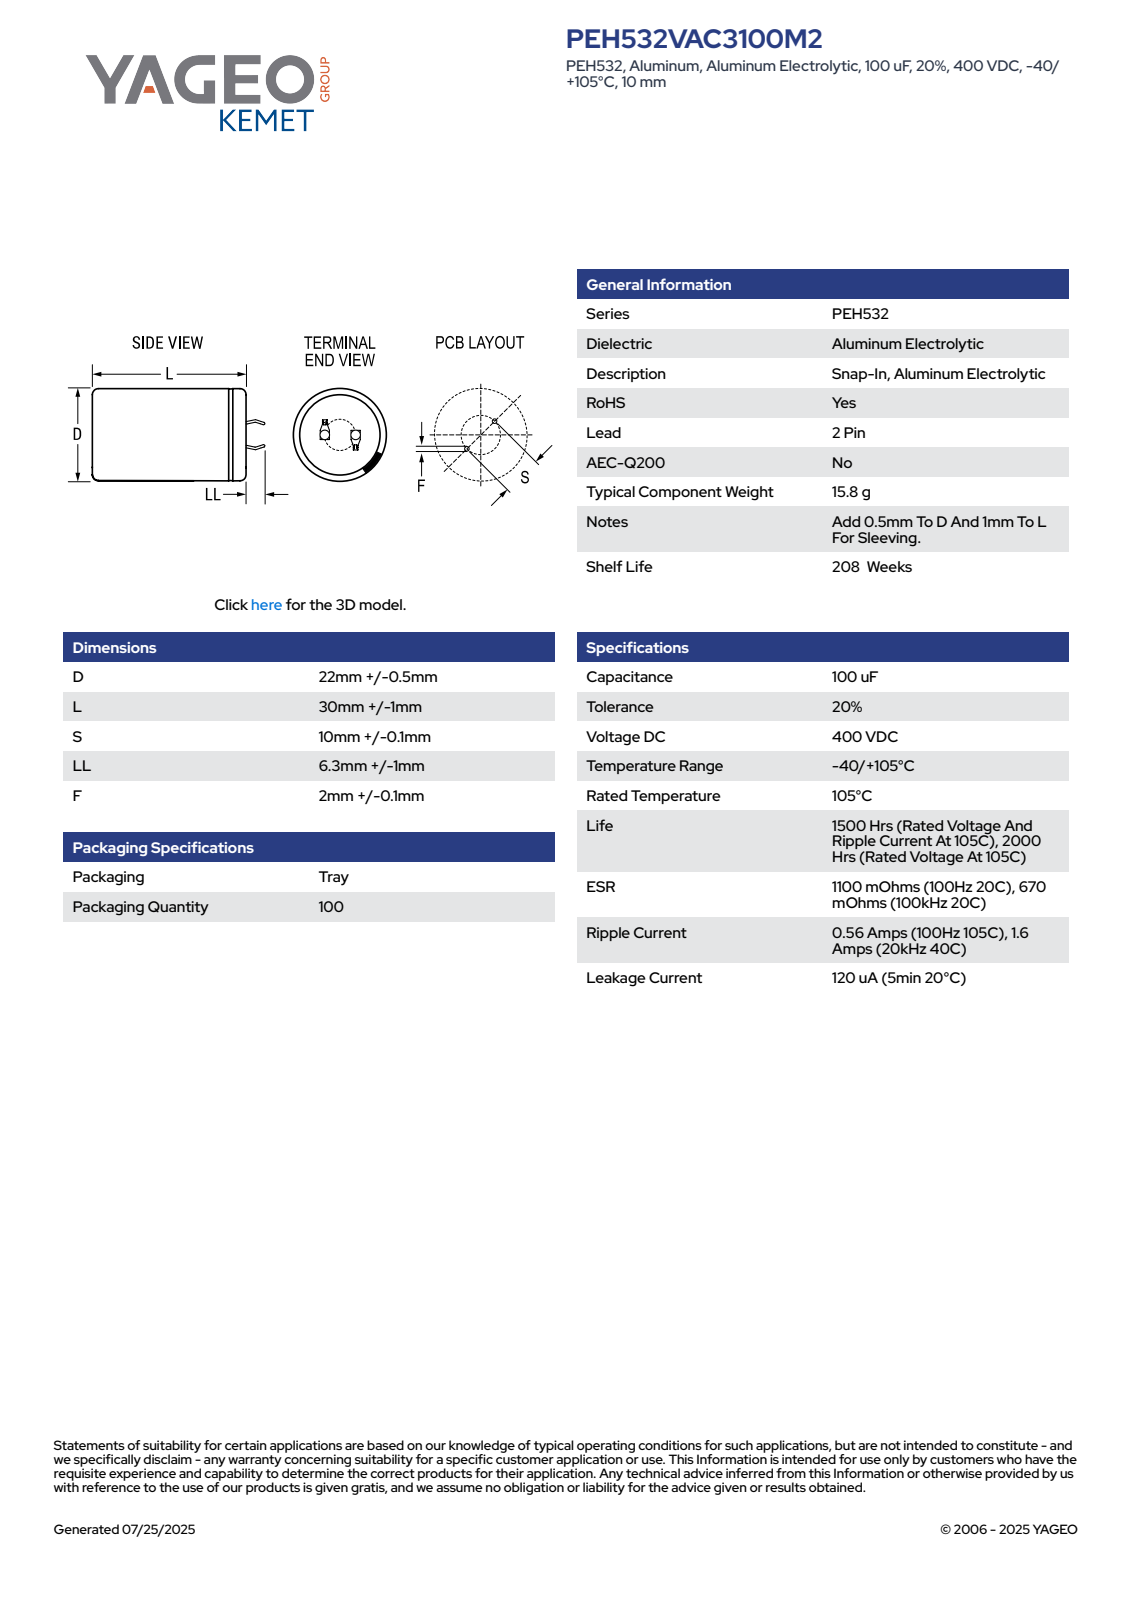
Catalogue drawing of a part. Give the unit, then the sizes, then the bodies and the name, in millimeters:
Units: millimetres
Overall size (bounding box): 38.29 × 22.5 × 22.5
Round holes (diameter × count): ⌀19.91 ×1
Round bosses / shafts (diameter × count): ⌀22.5 ×1
Partial cylindrical surfaces — rounded edges, fillets, slot ends (radius × count): R11.24 ×1
Main face-to-face distances: 30.99, 0.6, 31.49, 0.5, 7.08, 7.64, 0.75, 1.35, 7.68, 6.48
Volume: 12 205 mm³ · Surface area: 3 014 mm²
Bodies: 1 solid, 100 faces (52 planar, 9 cylindrical, 39 other)
Part name (STEP PRODUCT): CARS_K2P_22X30_D22.5L31S10LL7.3F2.1
STEP written by: SolidWorks 2014 (AUTOMOTIVE_DESIGN)
